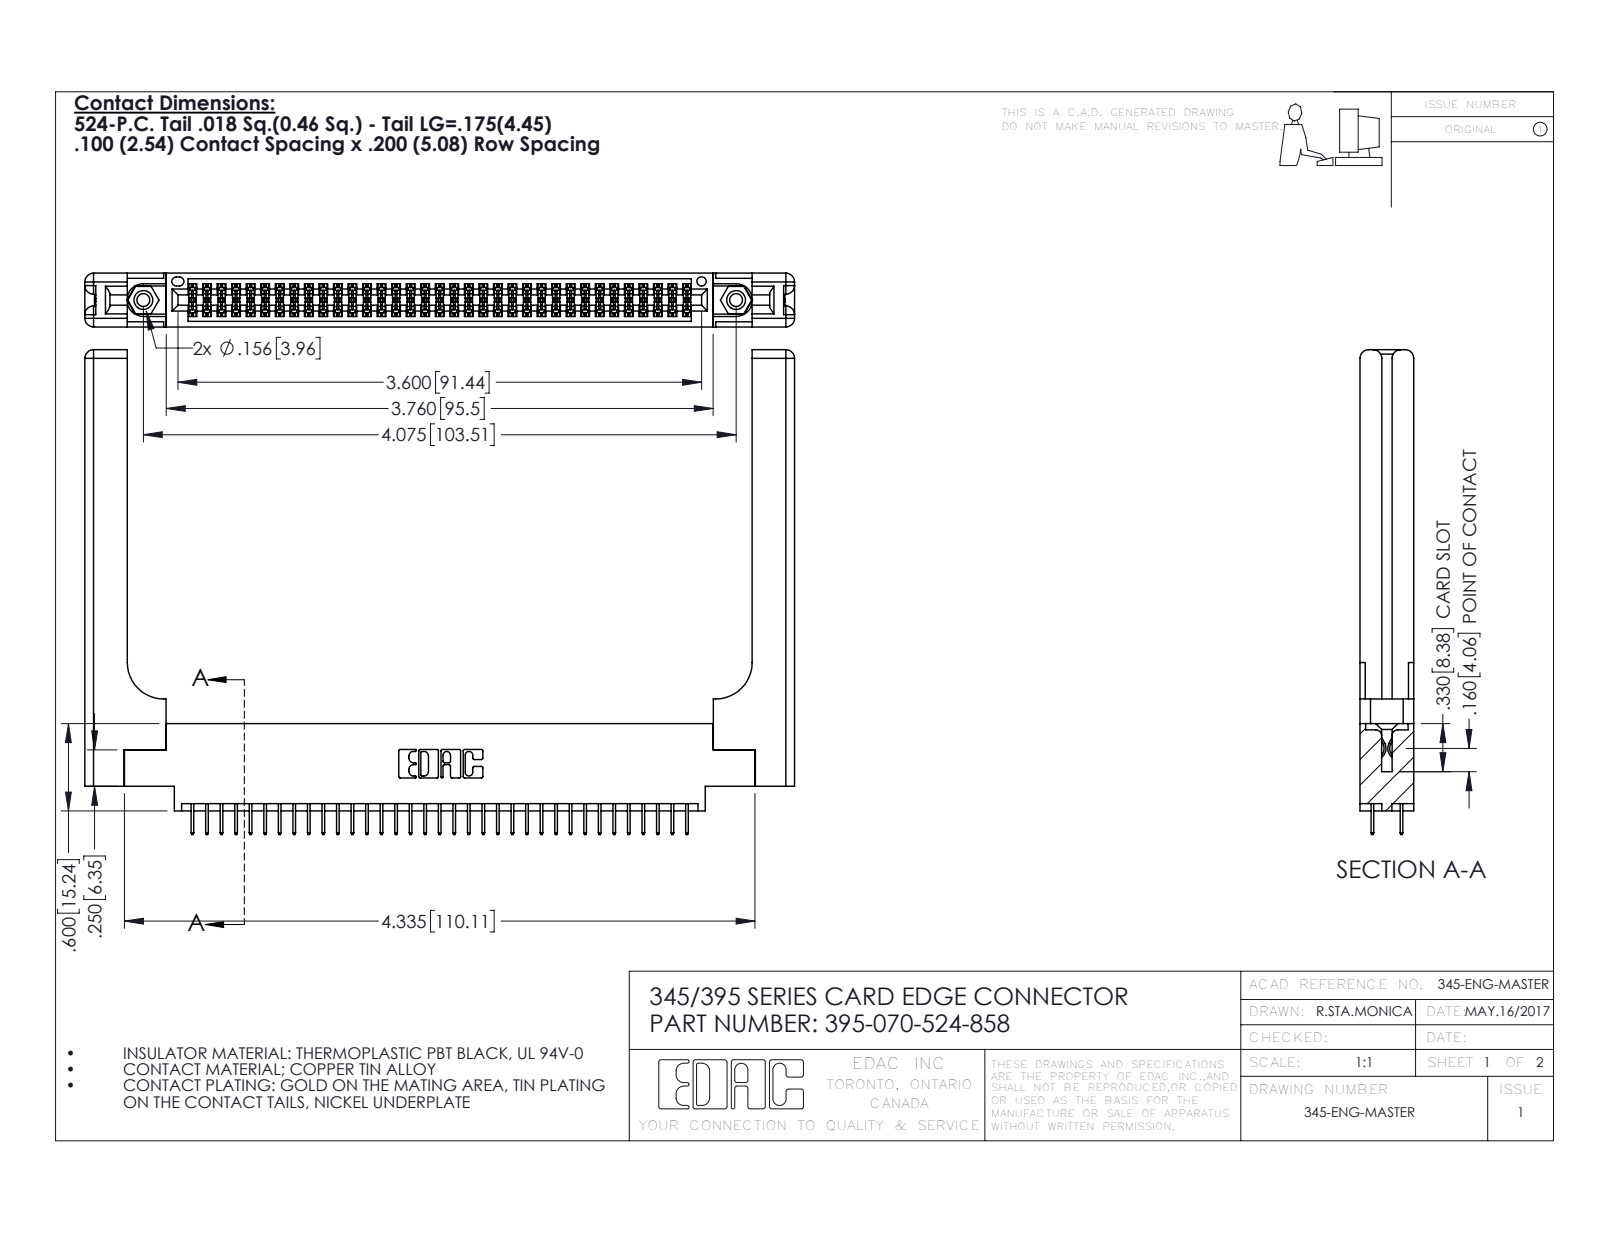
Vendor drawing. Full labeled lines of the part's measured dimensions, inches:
Part name (STEP PRODUCT): 395-070-524-858; 345-250-001_345-250-001-102; 345-292-001_345-293-124; 345 Part_0.170 Offset - 0.156 Dia-TH (+1 more)
STEP written by: SolidWorks 2016 (CONFIG_CONTROL_DESIGN)
Units: inches
Bodies: 75 solids, 4166 faces (2962 planar, 1144 cylindrical, 60 other)
Overall size (bounding box): 4.879 × 3.332 × 0.37
Volume: 1.234 in³ · Surface area: 34.35 in²
Round holes (diameter × count): ⌀0.089 ×2, ⌀0.125 ×2, ⌀0.156 ×2, ⌀0.064 ×1
Round bosses / shafts (diameter × count): ⌀0.155 ×2
Partial cylindrical surfaces — rounded edges, fillets, slot ends (radius × count): R0.006 ×105, R0.01 ×22, R0.06 ×16, R0.007 ×6, R0.031 ×6, R0.026 ×3, R0.014 ×2, R0.019 ×2
Main face-to-face distances: 0.37, 0.072, 0.298, 0.2, 0.098, 0.272, 0.025, 0.225, 0.148, 0.15
Hole centre spacings: 0.27, 3.839, 4.075
